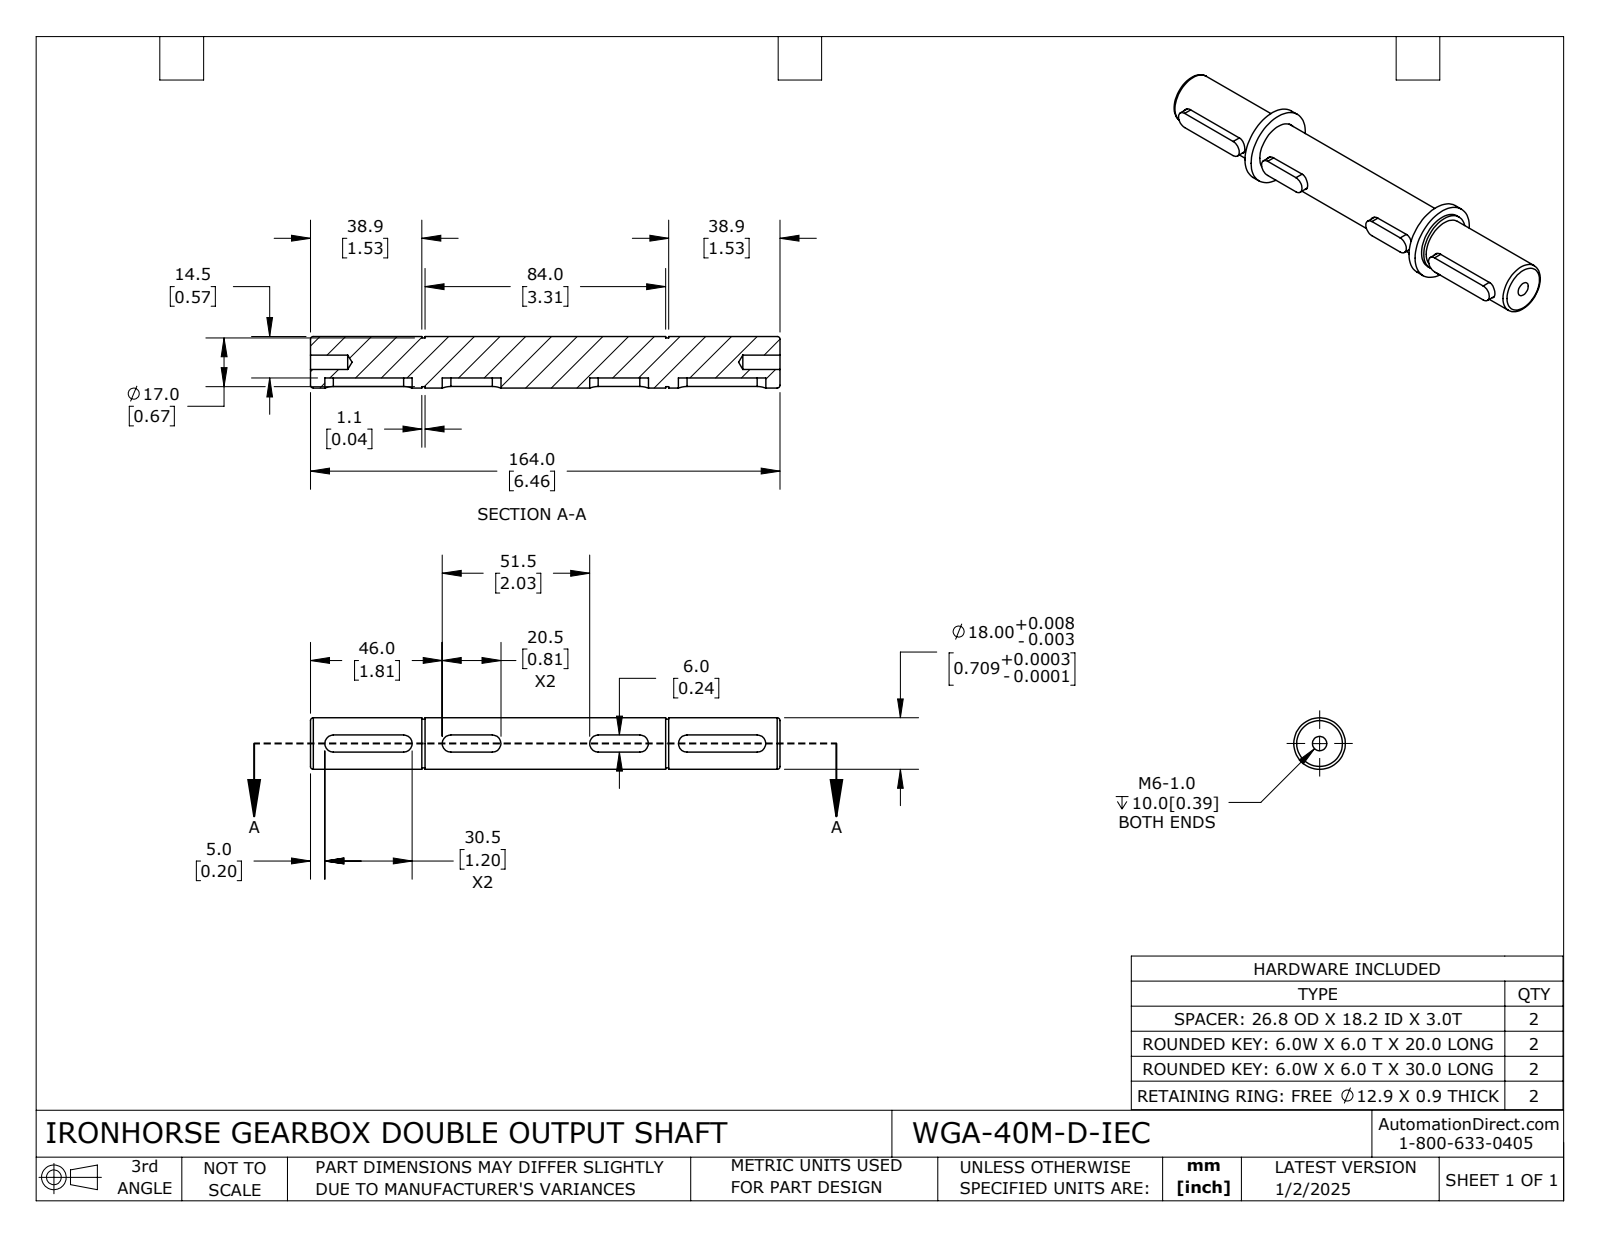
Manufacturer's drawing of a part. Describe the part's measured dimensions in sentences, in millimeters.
The part is named "WGA-40M-D-IEC". Its 3-D file was written by "SolidWorks 2024 (CONFIG_CONTROL_DESIGN)". It is 9 solids with 136 faces: 54 planar, 74 cylindrical and 8 other. Overall it measures 164 by 26.8 by 26.8 millimeters. Its volume is 44 664 cubic millimeters and its surface area 16 265 square millimeters. Round holes: 2 of diameter 1.3, 1 of diameter 5, 1 of diameter 17, 1 of diameter 18.2. Round bosses or shafts: 1 of diameter 26.8, 1 of diameter 20.45, 1 of diameter 18. Partial cylindrical surfaces (rounded edges, fillets, slot ends): 16 of radius 3, 2 of radius 0.5, 2 of radius 2.2. The main face-to-face distances are 6, 3, 81, 84, 40, 43, 121, 124, 78, 38.9. The hole center spacings are 10.48, 2.4.
